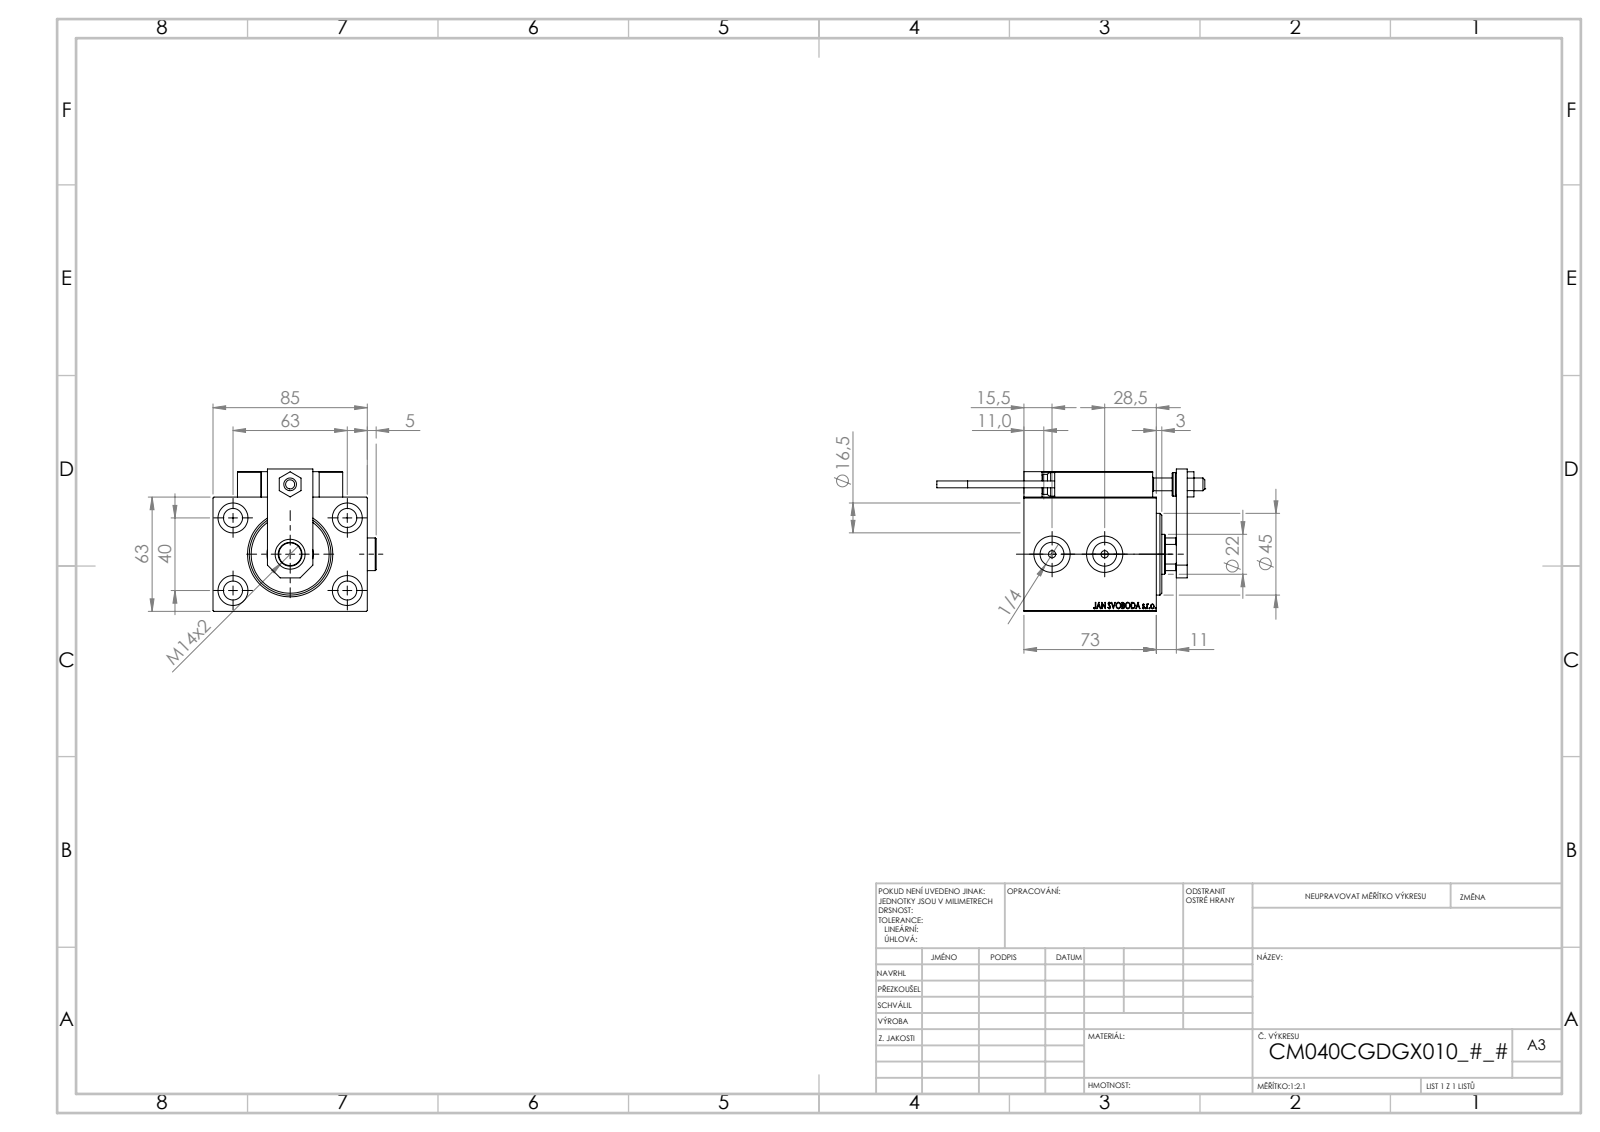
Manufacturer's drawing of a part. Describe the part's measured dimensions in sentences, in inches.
The part is named "SWITCH DIM B,W; V450CM_C_Body; ZARAZKA; NUT_D12 (+7 more)". Its 3-D file was written by "SolidWorks 2019 (CONFIG_CONTROL_DESIGN)". It is 25 solids with 1334 faces: 594 planar, 202 cylindrical and 538 other. Overall it measures 5.815 by 3.539 by 3.091 inches. Its volume is 23.94 cubic inches and its surface area 146.5 square inches. Round holes: 6 of diameter 0.157, 5 of diameter 0.315, 5 of diameter 0.65, 4 of diameter 0.126, 4 of diameter 0.413, 2 of diameter 0.197, 2 of diameter 0.518, 2 of diameter 0.787, 1 of diameter 0.276, 1 of diameter 0.492, 1 of diameter 0.866, 1 of diameter 1.004. Round bosses or shafts: 2 of diameter 0.709, 2 of diameter 0.197, 2 of diameter 0.15, 1 of diameter 0.512, 1 of diameter 0.433. Partial cylindrical surfaces (rounded edges, fillets, slot ends): 30 of radius 0.012, 2 of radius 0.118, 1 of radius 0.413. The main face-to-face distances are 2.48, 3.346, 0.551, 0.866, 2.008, 2.874, 0.433, 2.441, 3.031, 0.394. The hole center spacings are 1.469, 0.448, 0.787, 0.987, 1.165, 1.169, 1.311, 1.4.
